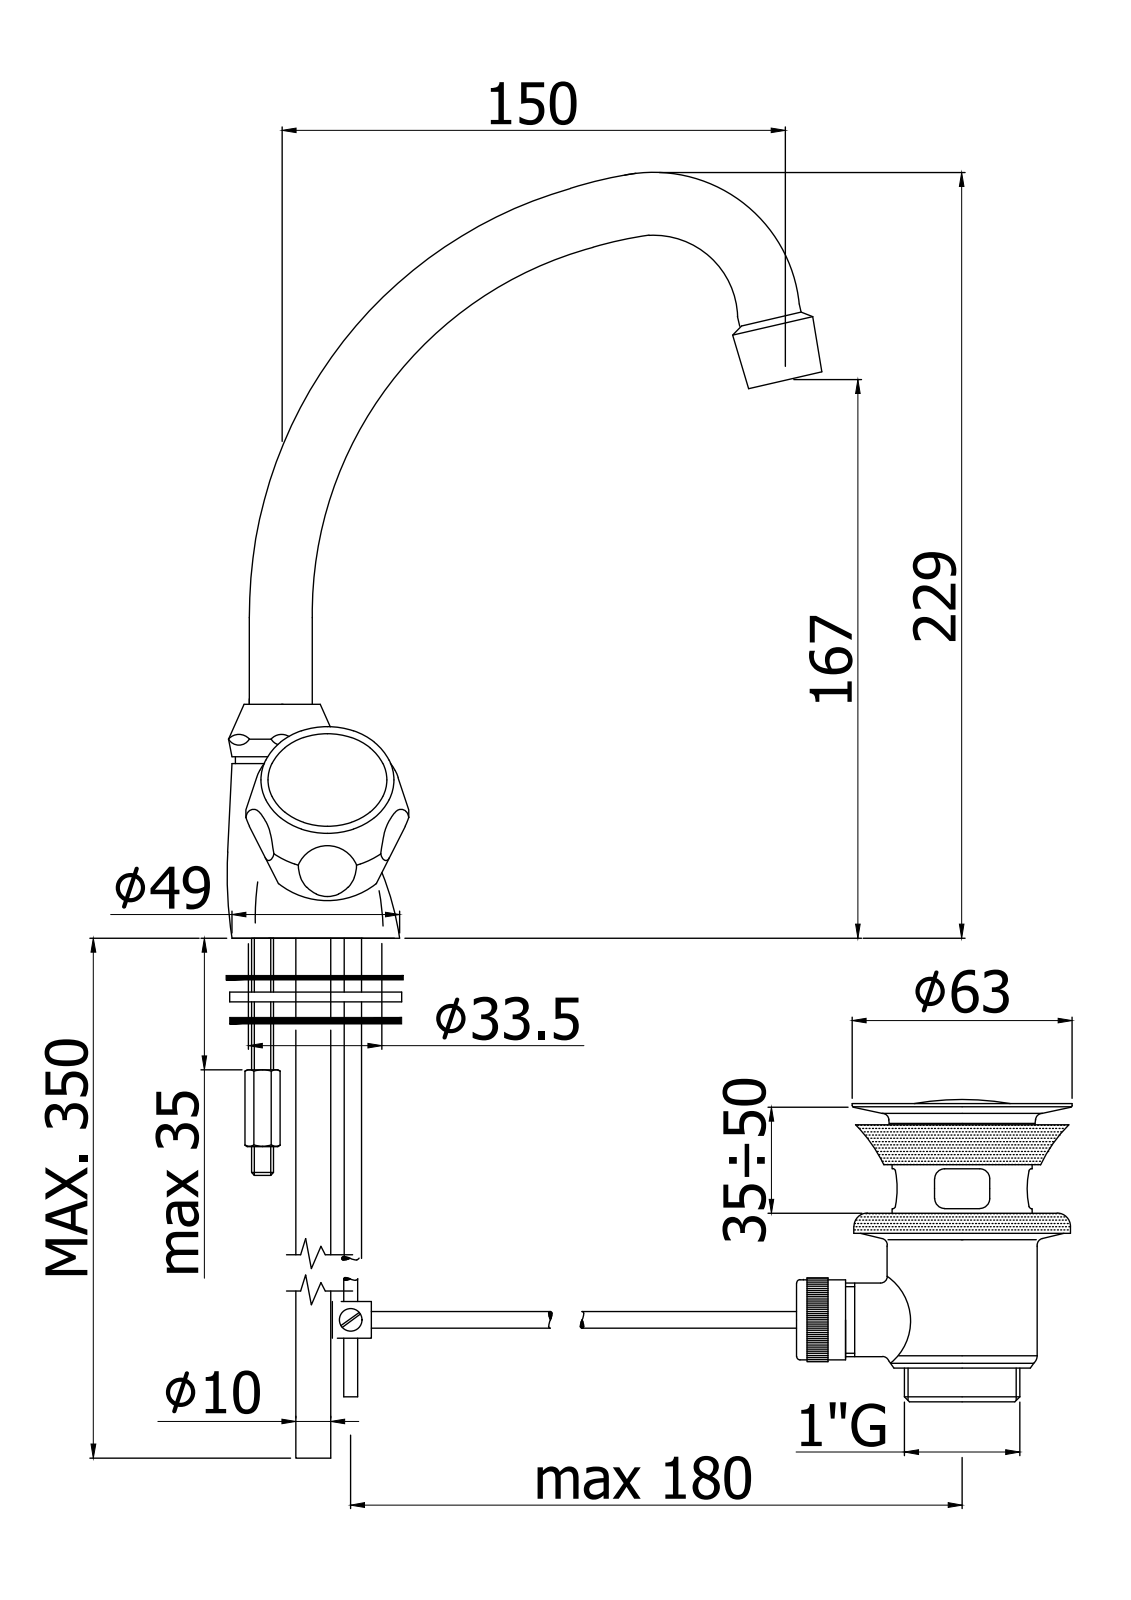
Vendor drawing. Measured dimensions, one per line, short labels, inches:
name: DA072CR
written by: CREO PARAMETRIC BY PTC INC, 2020044 (CONFIG_CONTROL_DESIGN)
unit: in
bodies: 2 solids, 318 faces (39 planar, 88 cylindrical, 191 other)
size: 8.996 × 7.065 × 5.718
volume: 15.34 in³; area: 82.55 in²
holes: 4× ⌀0.354, 2× ⌀0.433, 2× ⌀0.709, 2× ⌀0.748, 2× ⌀0.827, 2× ⌀0.846, 1× ⌀0.217, 1× ⌀0.236, 1× ⌀0.268, 1× ⌀0.472, 1× ⌀0.642, 1× ⌀0.713
bosses: 2× ⌀1.516, 2× ⌀1.035, 2× ⌀0.709, 1× ⌀1.339, 1× ⌀1.039, 1× ⌀0.929, 1× ⌀0.705, 1× ⌀0.354
rounds: 16× R0.839
face distances: 1.39, 1.406, 0.016, 0.799, 2.189, 2.205, 1.681, 0.051, 1.63, 0.039
hole spacings: 0.276, 0.465, 0.527, 0.547, 0.024, 0.374, 0.449, 0.472
